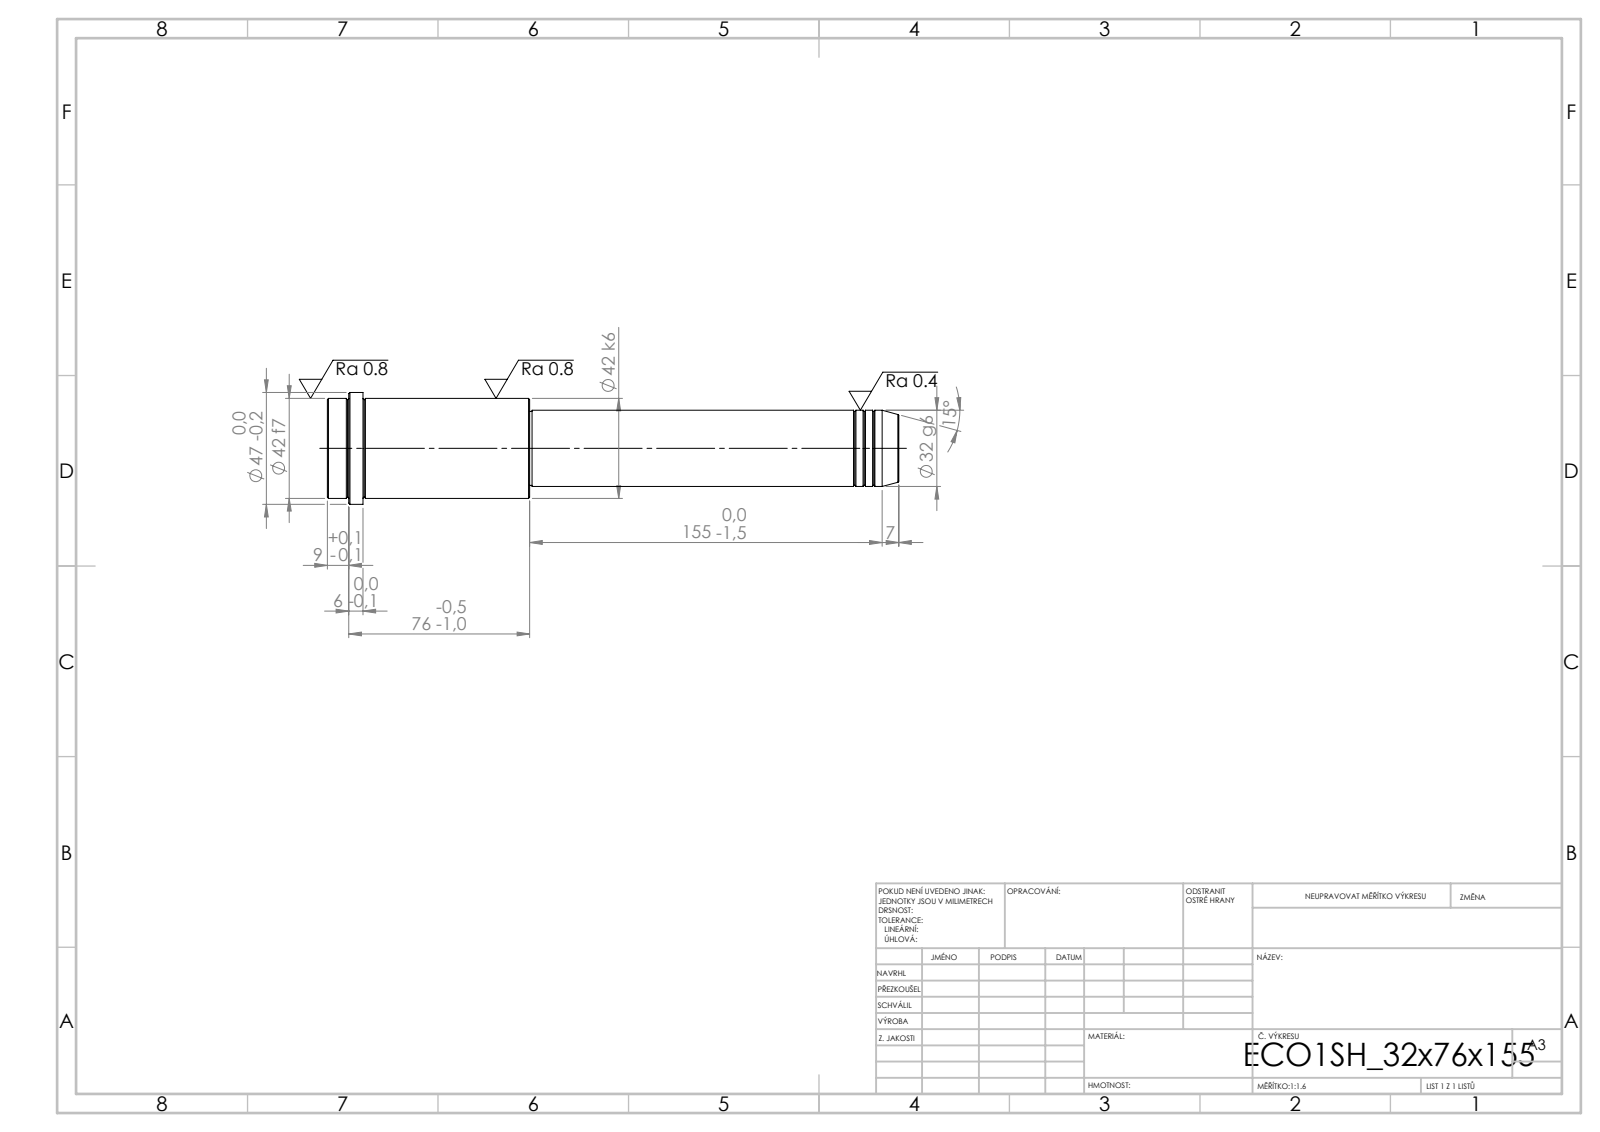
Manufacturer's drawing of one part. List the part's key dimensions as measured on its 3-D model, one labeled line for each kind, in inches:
STEP written by: SolidWorks 2019 (CONFIG_CONTROL_DESIGN)
Units: inches
Bodies: 1 solid, 52 faces (6 planar, 16 cylindrical, 30 other)
Overall size (bounding box): 9.449 × 1.85 × 1.85
Volume: 14.86 in³ · Surface area: 47.18 in²
Round bosses / shafts (diameter × count): ⌀1.85 ×1, ⌀1.654 ×1, ⌀1.26 ×1, ⌀1.22 ×1
Main face-to-face distances: 9.449, 6.102, 3.346, 8.858, 2.756, 0.591, 9.094, 2.992, 0.236, 0.354
